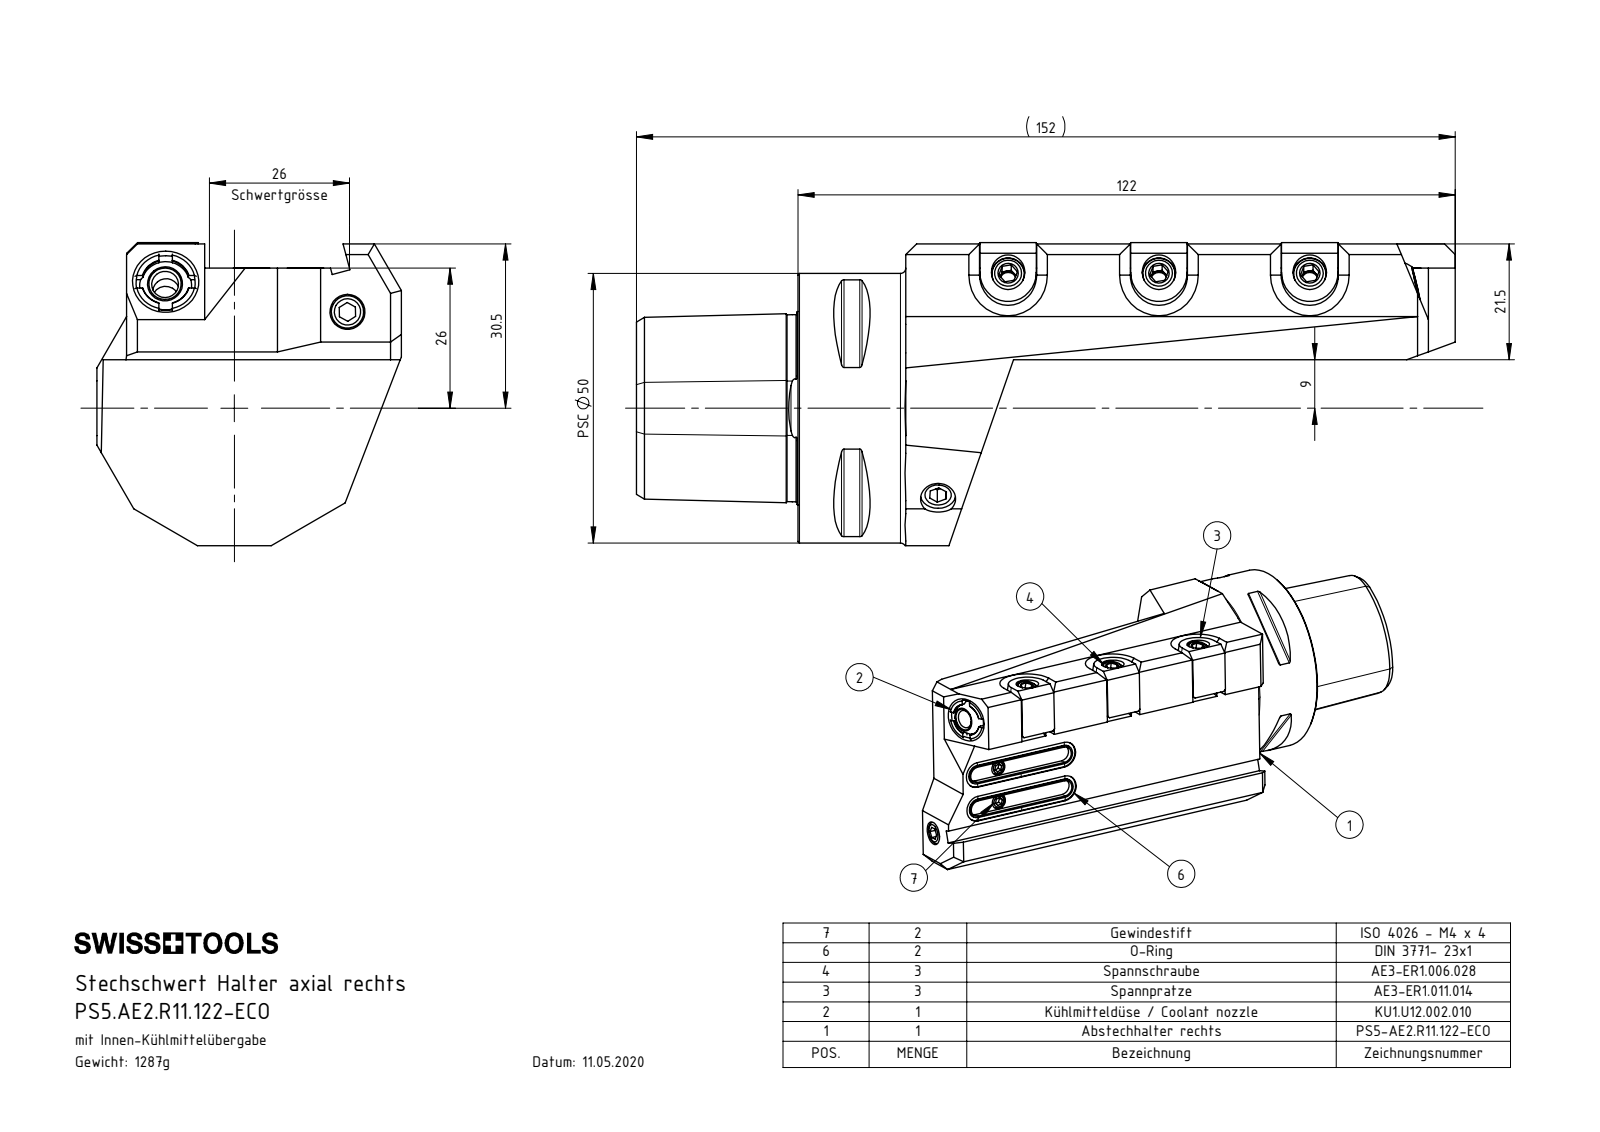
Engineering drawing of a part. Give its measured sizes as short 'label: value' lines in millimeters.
name: PS5-AE2.R11.122-ECO; Teil6; DIN 3771 - 8x1.5; PS5-AE2.R11.122-ECO_A (+6 more)
written by: SolidWorks 2017 (AUTOMOTIVE_DESIGN)
unit: mm
bodies: 15 solids, 425 faces (223 planar, 83 cylindrical, 119 other)
size: 152 × 57.5 × 56.5
volume: 169 717 mm³; area: 40 760 mm²
holes: 7× ⌀5, 6× ⌀6.8, 3× ⌀3, 3× ⌀5.5, 2× ⌀3.3, 1× ⌀4, 1× ⌀6.1, 1× ⌀10, 1× ⌀11, 1× ⌀14.5, 1× ⌀21, 1× ⌀24
bosses: 6× ⌀6, 4× ⌀1, 3× ⌀4.5, 1× ⌀50, 1× ⌀12
rounds: 8× R0.5, 4× R2.25, 4× R2.65, 4× R3.65, 3× R5.25, 1× R4, 1× R4.4
face distances: 17.5, 4.5, 22, 51, 26, 10.5, 20, 30, 52, 4.48
hole spacings: 26, 10, 27.59, 52, 95.9, 121.49
